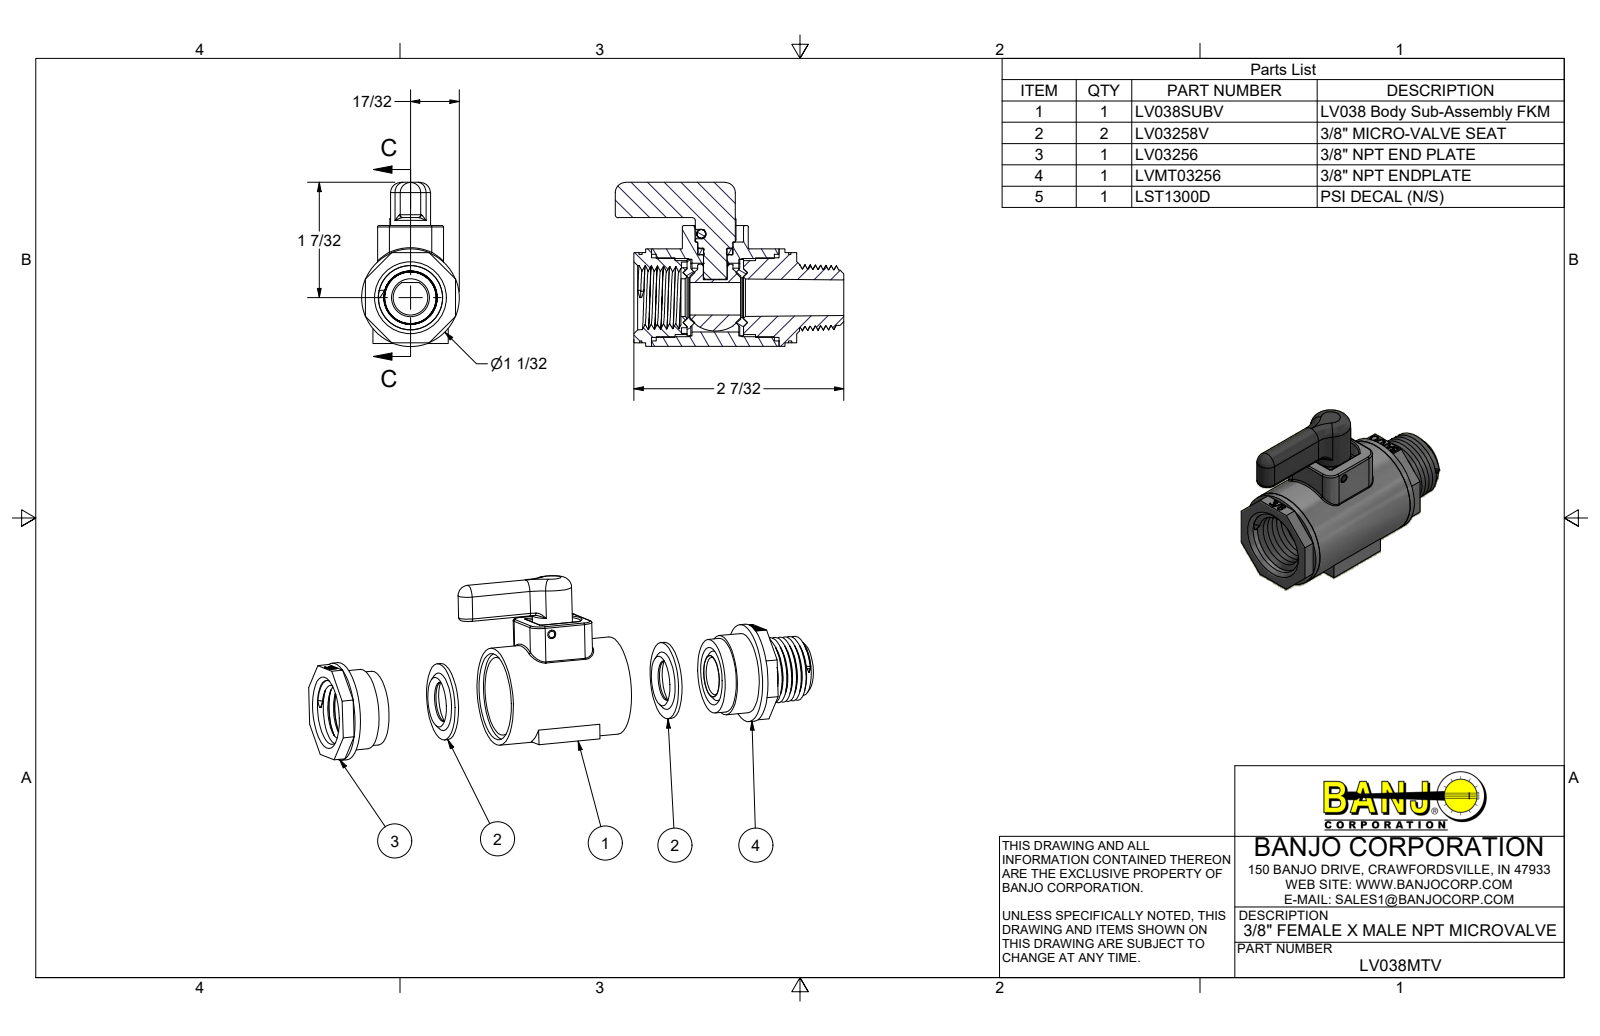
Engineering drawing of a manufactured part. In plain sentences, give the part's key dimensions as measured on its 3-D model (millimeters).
The part is named "LV038MTV; LV038SUBV; LV03254A; AQ010V (+6 more)". Its 3-D file was written by "Autodesk Inventor 2012 (AUTOMOTIVE_DESIGN)". It is 9 solids with 717 faces: 286 planar, 106 cylindrical and 325 other. Overall it measures 61.6 by 44.3 by 26.3 millimeters. Its volume is 23 710 cubic millimeters and its surface area 18 100 square millimeters. Round holes: 4 of diameter 1.5, 1 of diameter 2.4, 1 of diameter 6.4, 1 of diameter 9.3, 1 of diameter 9.4, 1 of diameter 9.6, 1 of diameter 10.2, 1 of diameter 10.7, 1 of diameter 18.5, 1 of diameter 20.7, 1 of diameter 21.1, 1 of diameter 23.4. Round bosses or shafts: 1 of diameter 26.3, 1 of diameter 21.5, 1 of diameter 20.6, 1 of diameter 19.9, 1 of diameter 10.8, 1 of diameter 9.5, 1 of diameter 9.4, 1 of diameter 6.4. Partial cylindrical surfaces (rounded edges, fillets, slot ends): 16 of radius 0.3, 14 of radius 0.4, 4 of radius 3.2, 2 of radius 0.8, 2 of radius 1.3, 2 of radius 2.8, 2 of radius 6.4, 1 of radius 1.2. The main face-to-face distances are 24.8, 9.6, 1.3, 4.8, 14.4, 29.6, 39.2, 8.3, 34.4, 15.4. The hole center spacings are 8.9, 12.5, 17.8.
